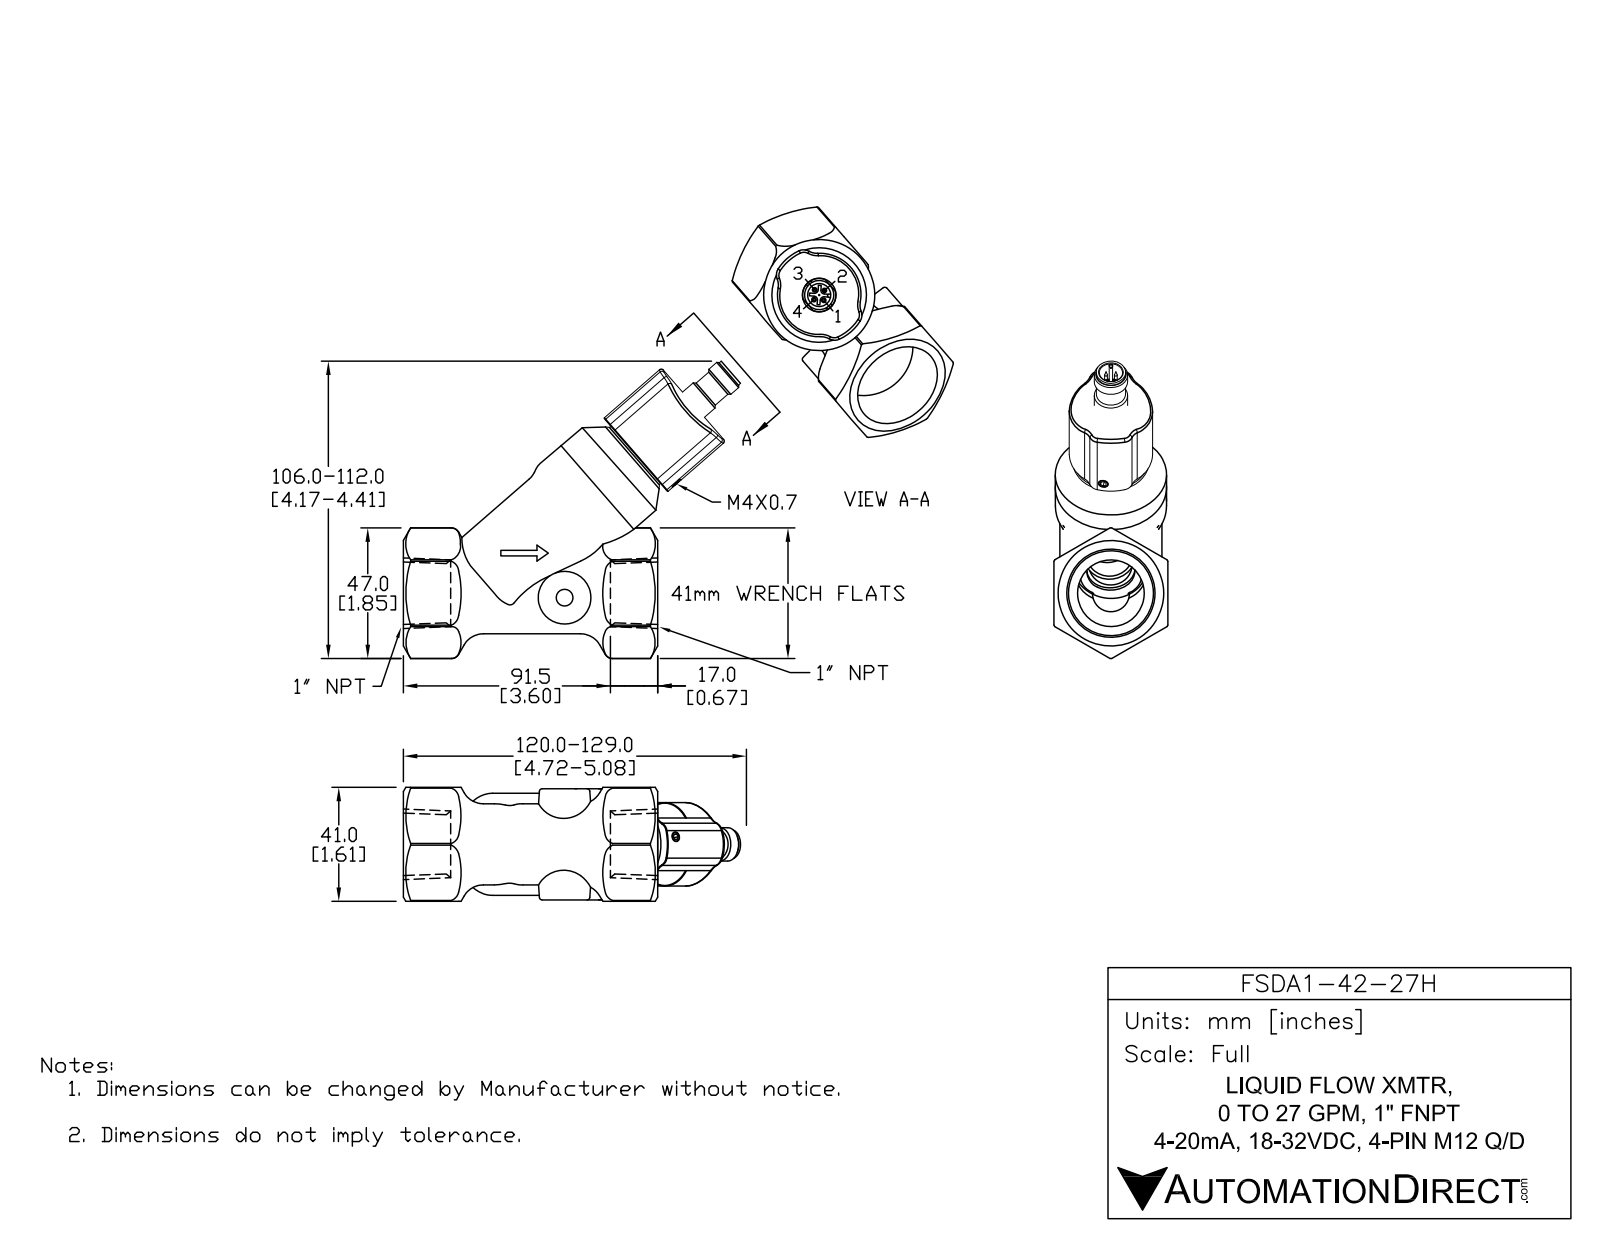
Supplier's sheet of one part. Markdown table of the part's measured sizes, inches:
| quantity | value |
| --- | --- |
| part name | FSA1-41-27H |
| STEP written by | SolidWorks 2021 (AUTOMOTIVE_DESIGN) |
| units | inches |
| bodies | 1 solid, 172 faces (59 planar, 73 cylindrical, 40 other) |
| overall size | 4.856 × 4.349 × 1.732 |
| volume | 9.129 in³ |
| surface area | 53.29 in² |
| round holes (diameter × count) | 0.283 × 2, 0.327 × 1, 1.15 × 1, 1.193 × 1 |
| round bosses / shafts (diameter × count) | 1.575 × 1, 1.059 × 1, 0.472 × 1, 0.417 × 1, 0.413 × 1 |
| partial cylindrical surfaces (radius × count) | 0.098 × 4, 0.157 × 4, 0.236 × 4, 0.079 × 2, 0.098 × 2, 0.197 × 2, 0.866 × 2, 0.024 × 1 |
| main face-to-face distances | 1.591, 0.071, 1.661, 2.965, 0.638, 0.591, 1.142, 0.52, 1.071, 1.732 |
| hole center spacings | 1.063 |
